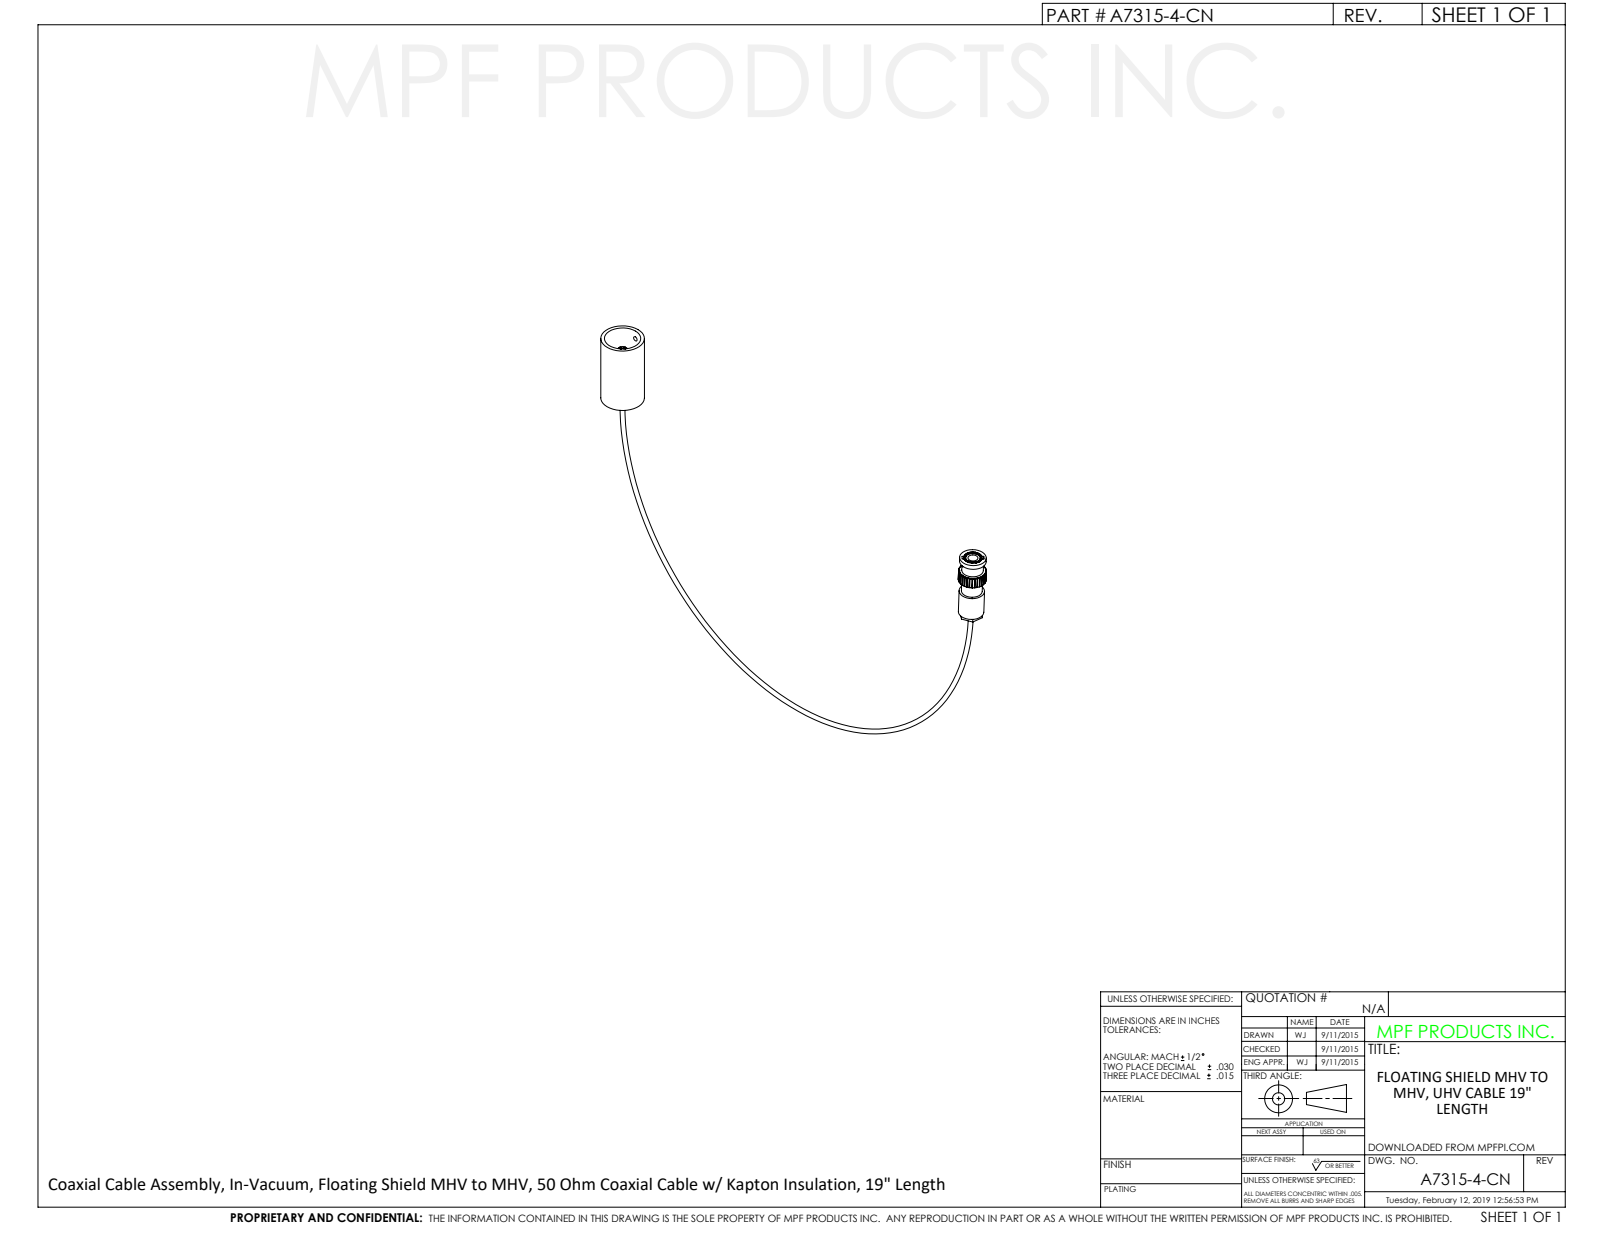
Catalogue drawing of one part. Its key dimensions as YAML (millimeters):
part_name: "A7315-4-CN; A0060-2; A7309-1-CN_110183"
step_written_by: "SolidWorks 2012 (CONFIG_CONTROL_DESIGN)"
units: millimeters
bodies: {solids: 2, faces: 348, planar: 240, cylindrical: 104, other: 4}
overall_size: [278.6, 173.6, 25.4]
volume: 18530
surface_area: 11150
round_holes:
  - {diameter: 2.5, count: 3}
  - {diameter: 1.9, count: 1}
  - {diameter: 4, count: 1}
  - {diameter: 4.9, count: 1}
  - {diameter: 5.1, count: 1}
  - {diameter: 9.9, count: 1}
  - {diameter: 19.1, count: 1}
round_bosses_or_shafts:
  - {diameter: 25.4, count: 1}
  - {diameter: 14, count: 1}
  - {diameter: 13.3, count: 1}
  - {diameter: 11.3, count: 1}
  - {diameter: 10.9, count: 1}
  - {diameter: 7.8, count: 1}
  - {diameter: 5.1, count: 1}
partial_cylinders:
  - {radius: 1.7, count: 1}
  - {radius: 3.8, count: 1}
  - {radius: 3.8, count: 1}
  - {radius: 7.3, count: 1}
face_to_face_distances: [38.1, 8.3, 24.8, 0.4, 16.6, 22.3, 5.7, 2.5, 9.8, 6.8]
hole_center_spacings: [8.9]
